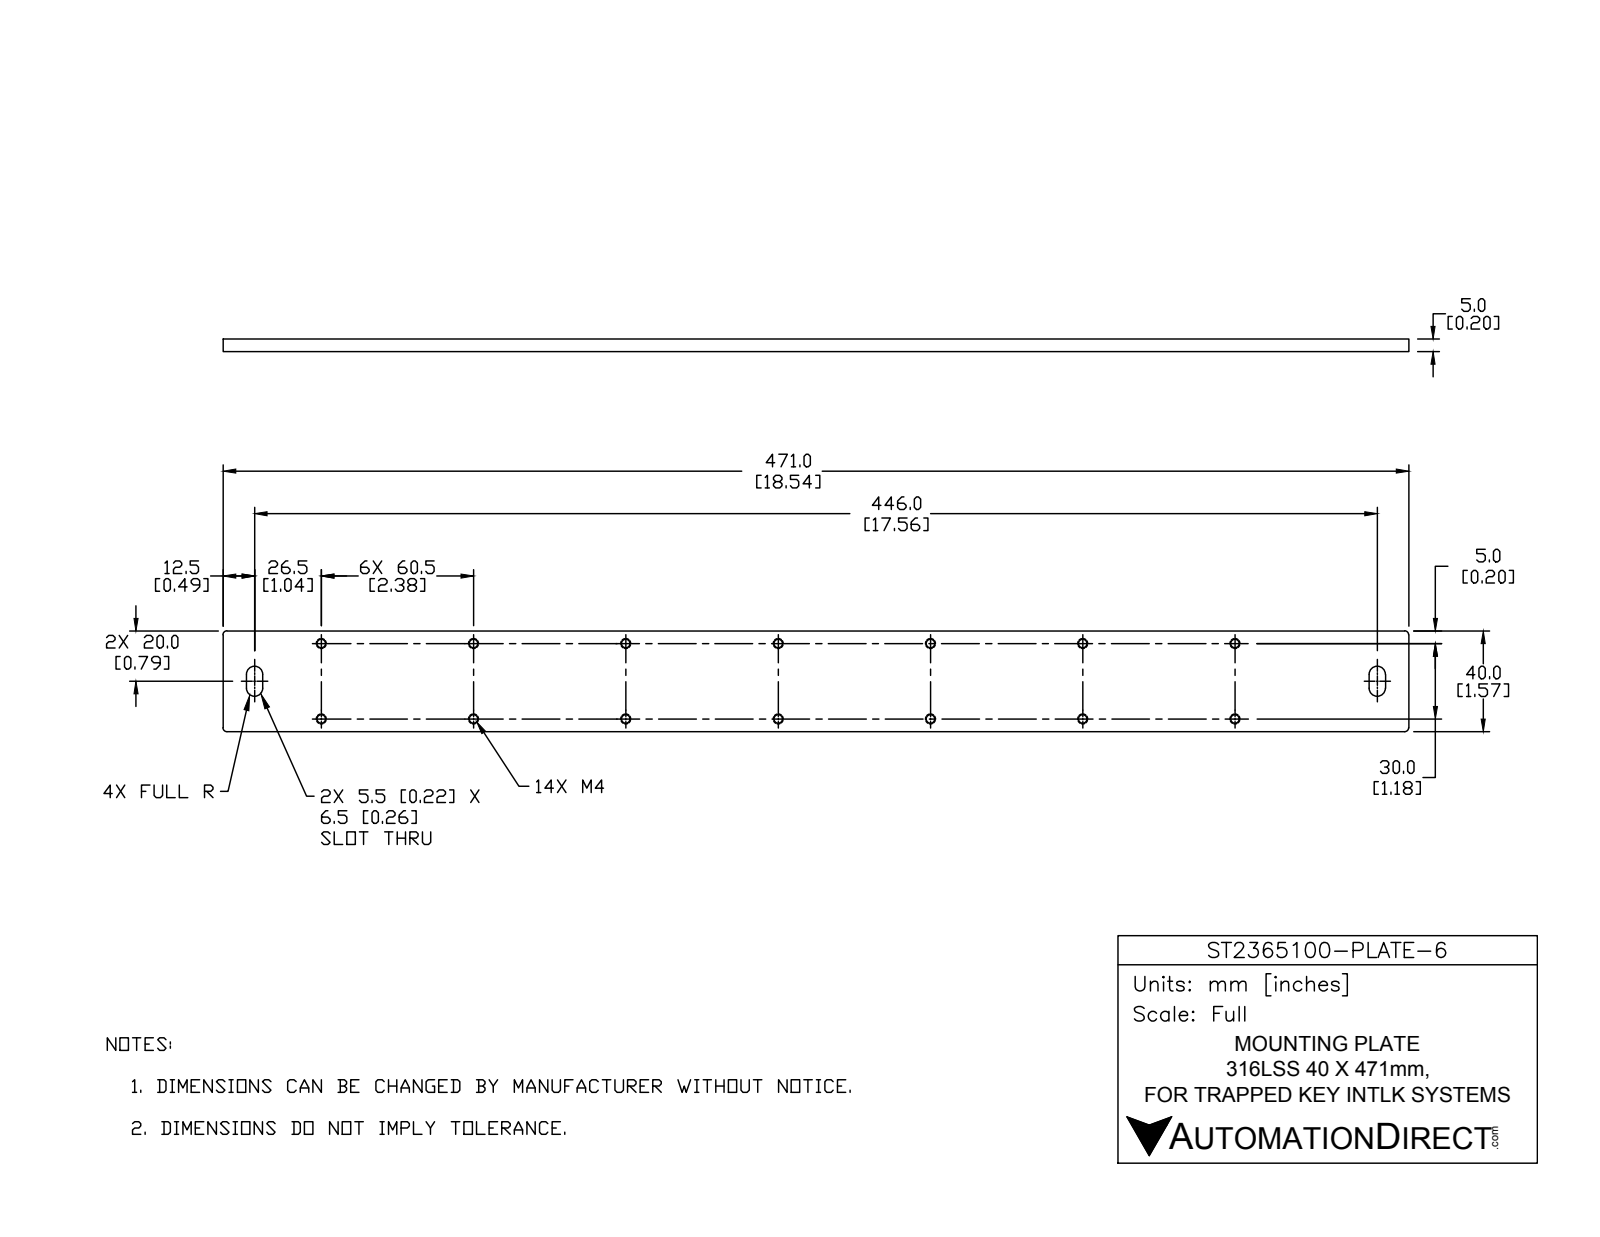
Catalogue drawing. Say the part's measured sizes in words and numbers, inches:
The part is named "ST2365100-PLATE-6". Its 3-D file was written by "SolidWorks 2017 (AUTOMOTIVE_DESIGN)". It is 1 solid with 64 faces: 10 planar, 38 cylindrical and 16 other. Overall it measures 18.543 by 1.575 by 0.197 inches. Its volume is 5.663 cubic inches and its surface area 66.4 square inches. Round holes: 14 of diameter 0.128. Partial cylindrical surfaces (rounded edges, fillets, slot ends): 8 of radius 0.008, 8 of radius 0.02, 4 of radius 0.079, 4 of radius 0.128. The main face-to-face distances are 0.197, 1.575, 18.543, 0.364, 0.62, 17.923, 18.179, 0.256, 17.559, 17.815. The hole center spacings are 2.362, 2.641, 4.724, 4.87, 7.087, 7.184, 1.181, 9.449.
